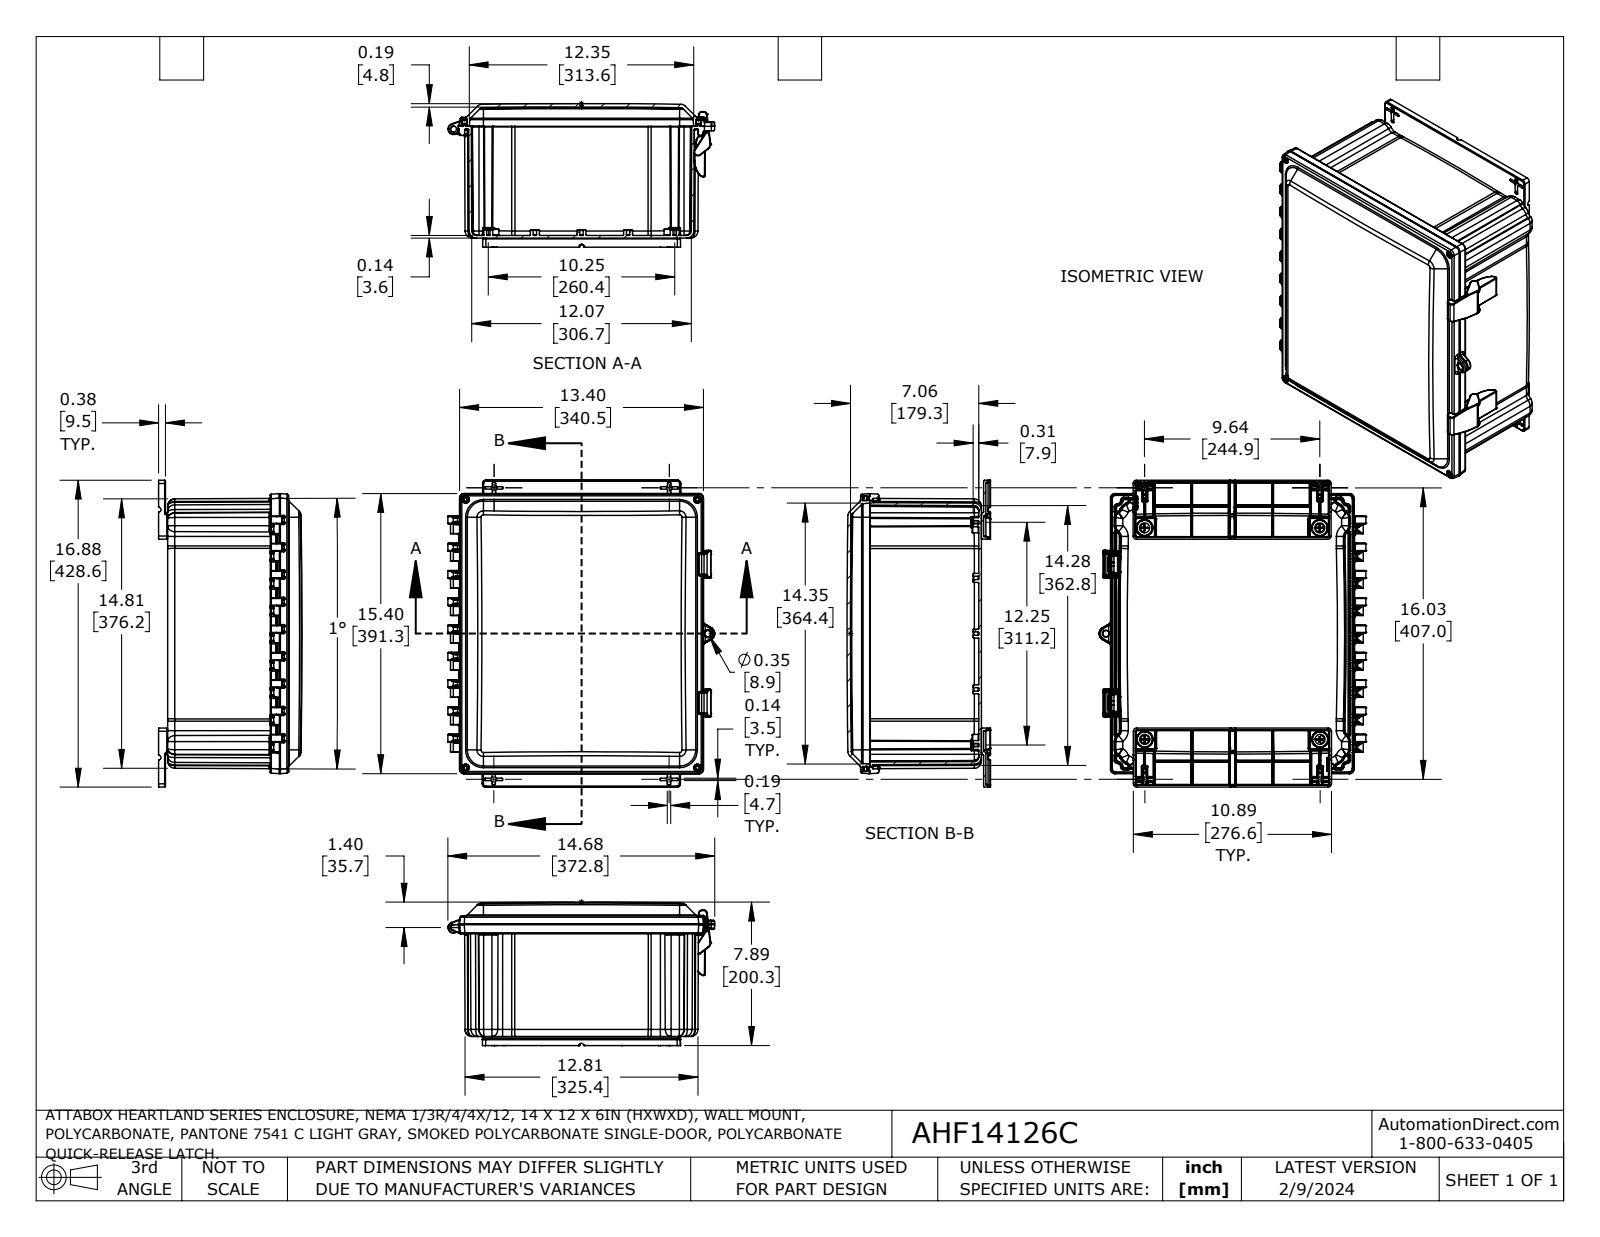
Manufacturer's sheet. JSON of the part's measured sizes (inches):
{"part_name": "AHF14126C", "step_written_by": "SolidWorks 2023 (AUTOMOTIVE_DESIGN)", "units": "inches", "bodies": {"solids": 6, "faces": 1694, "planar": 583, "cylindrical": 533, "other": 578}, "overall_size": [16.875, 14.676, 7.888], "volume_in3": 167.3, "surface_area_in2": 1805, "round_holes": [[0.187, 21], [0.195, 4], [0.25, 4], [0.26, 4], [0.39, 4], [0.27, 2], [0.327, 1], [0.375, 1], [0.45, 1]], "round_bosses_or_shafts": [[0.487, 21], [0.625, 4], [0.25, 2], [0.2, 2], [0.313, 1]], "partial_cylinders_radius": [[0.035, 194], [0.065, 23], [0.01, 22], [0.02, 20], [0.338, 16], [0.05, 8], [0.413, 8], [0.09, 4]], "face_to_face_distances": [0.115, 0.14, 12.115, 0.5, 6.14, 14.115, 6.64, 12, 6, 0.64], "hole_center_spacings": [3.993, 5.97, 3.063, 8.275, 2.563, 3.993, 6.639, 6.64]}
